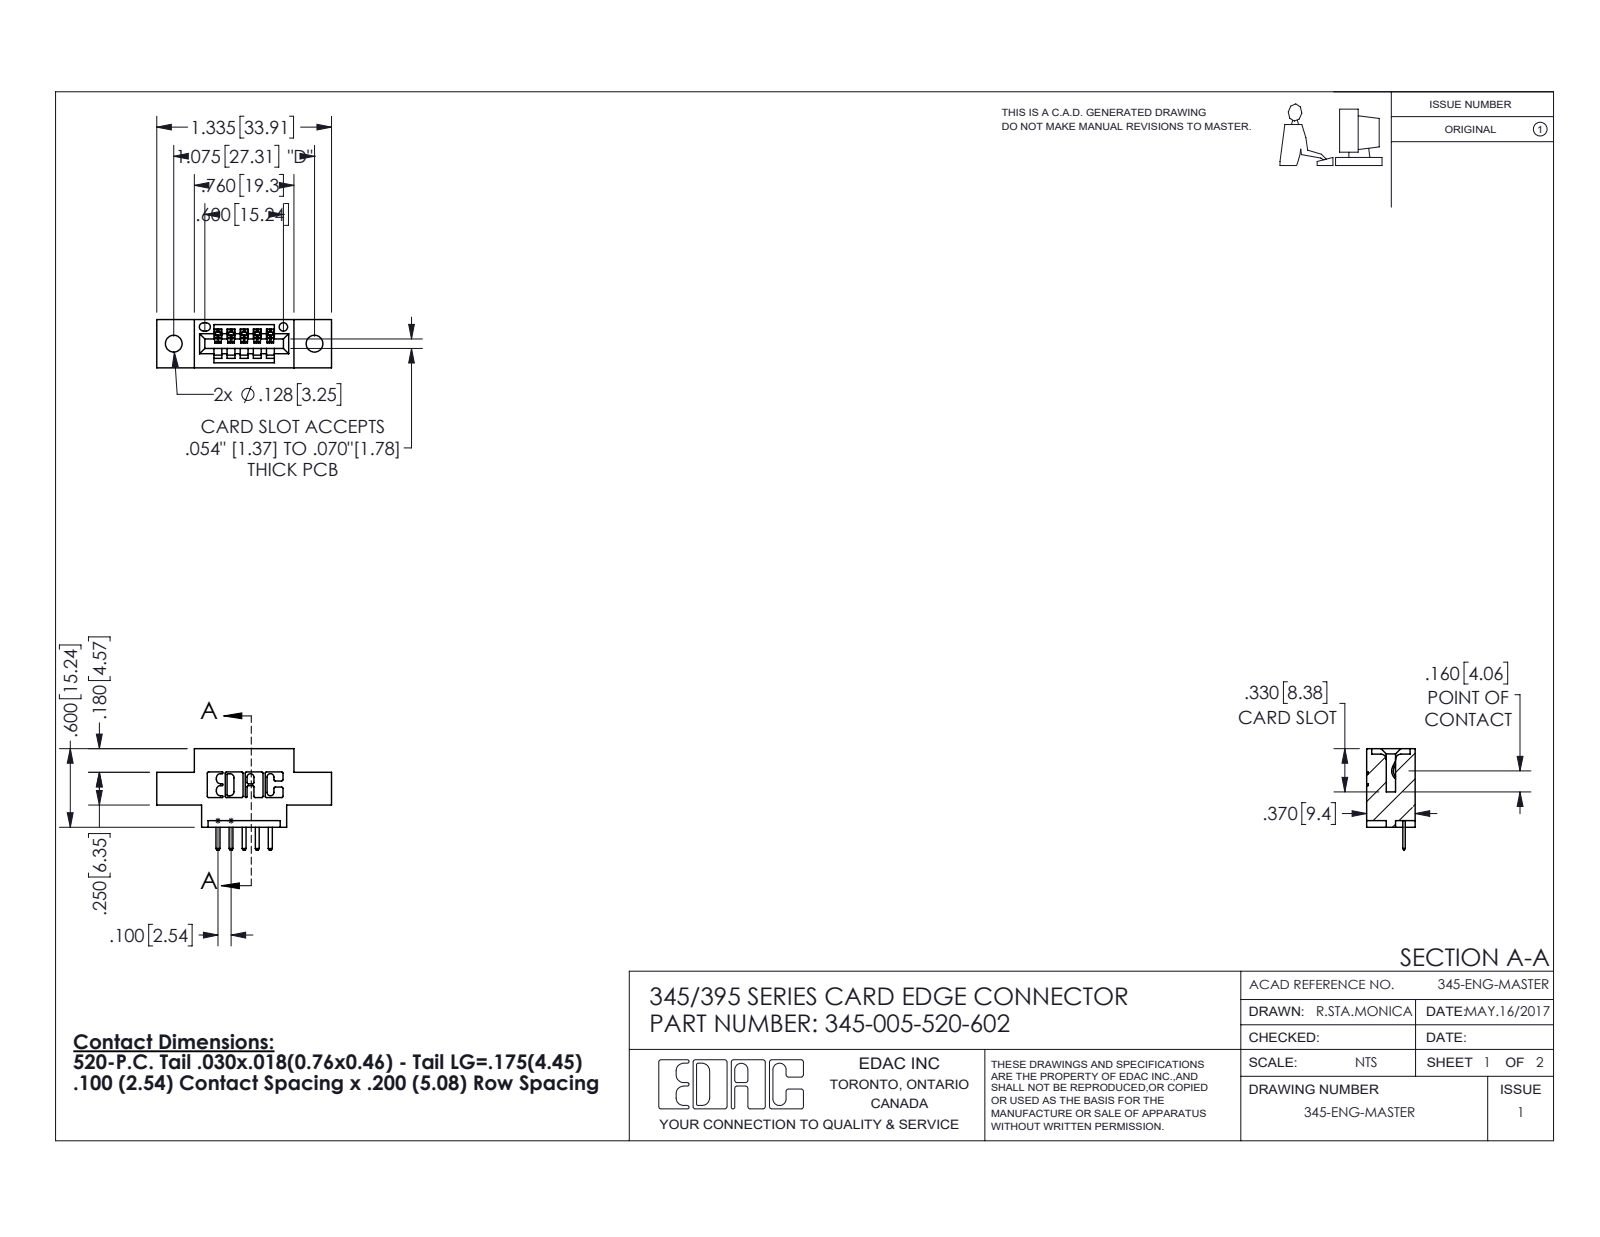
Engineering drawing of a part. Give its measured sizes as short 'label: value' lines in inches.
name: 345 Part_0.170 Offset - 0.128 Dia; 345-292-001_345-293-120; 345-005-520-602
written by: SolidWorks 2016 (CONFIG_CONTROL_DESIGN)
unit: in
bodies: 6 solids, 440 faces (294 planar, 146 cylindrical, 0 other)
size: 1.335 × 0.775 × 0.37
volume: 0.168 in³; area: 4.594 in²
holes: 2× ⌀0.128, 1× ⌀0.064
rounds: 22× R0.01, 12× R0.01, 10× R0.006, 6× R0.007, 6× R0.031, 3× R0.026, 2× R0.031, 2× R0.04
face distances: 0.37, 0.2, 0.1, 0.298, 0.072, 0.25, 0.025, 0.06, 0.55, 0.15
hole spacings: 0.27, 0.847, 1.075
